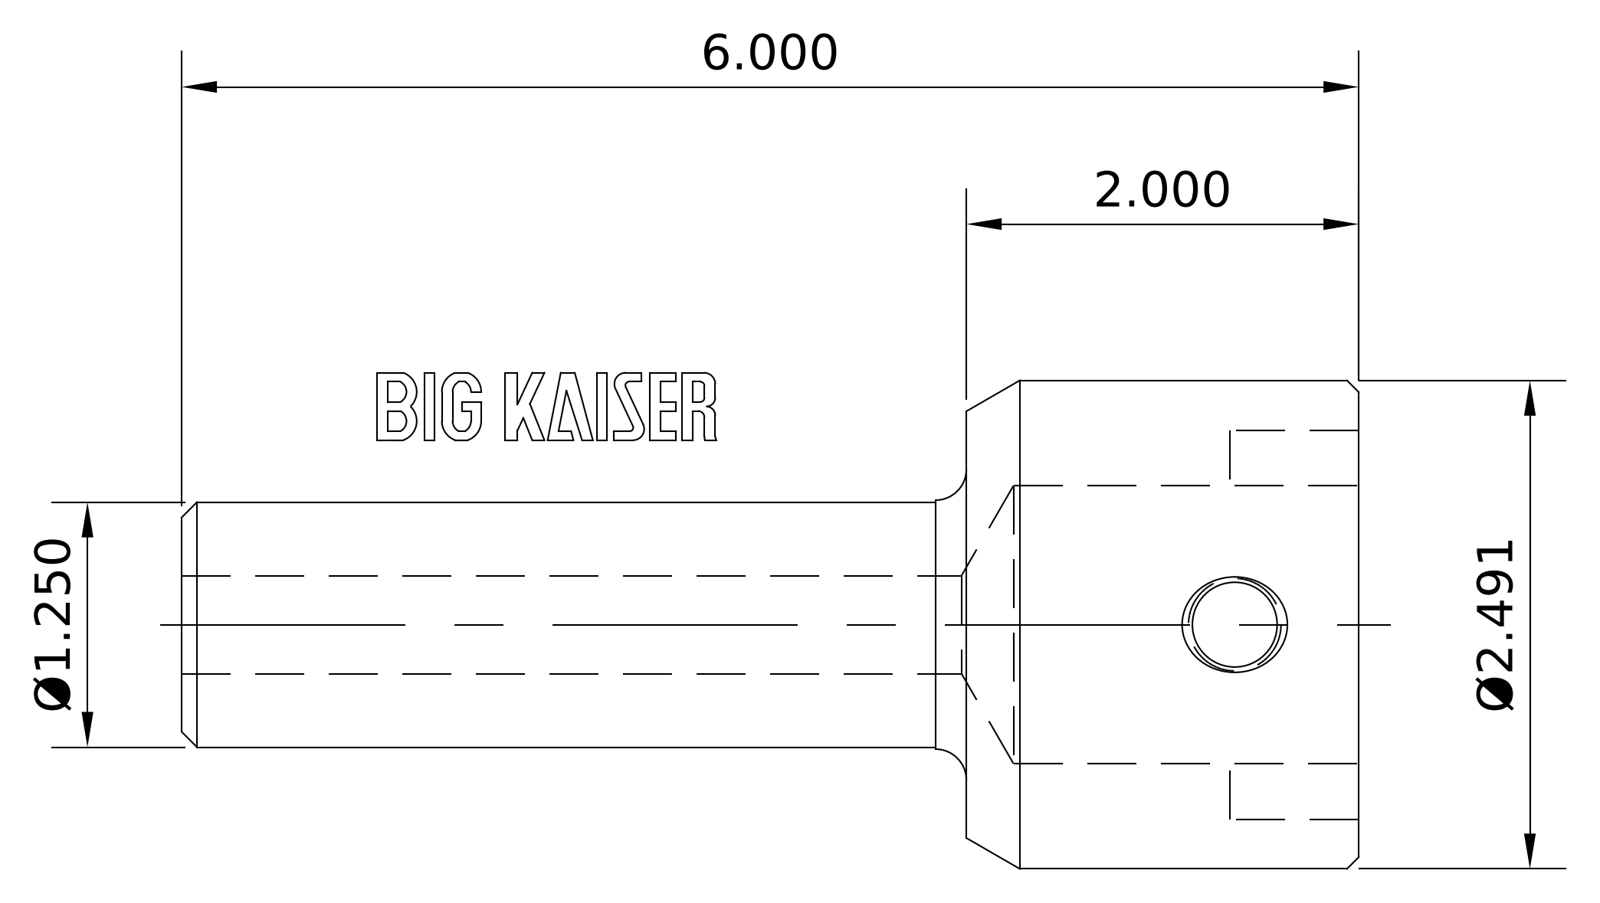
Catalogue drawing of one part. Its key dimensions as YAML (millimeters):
part_name: "11.361.162"
step_written_by: "SolidWorks 2018 (CONFIG_CONTROL_DESIGN)"
units: millimeters
bodies: {solids: 1, faces: 44, planar: 22, cylindrical: 10, other: 12}
overall_size: [152.4, 63.27, 63.27]
volume: 161933
surface_area: 35554
round_holes:
  - {diameter: 10.2, count: 1}
  - {diameter: 11.13, count: 1}
  - {diameter: 12.3, count: 1}
  - {diameter: 14.4, count: 1}
  - {diameter: 36, count: 1}
  - {diameter: 36.5, count: 1}
round_bosses_or_shafts:
  - {diameter: 63.27, count: 1}
  - {diameter: 31.75, count: 1}
partial_cylinders:
  - {radius: 5.5, count: 2}
face_to_face_distances: [50.8, 101.6, 152.4, 30.7, 16.44, 135.8, 34.2, 16.6, 7.19, 10.33]
hole_center_spacings: [25.05]
